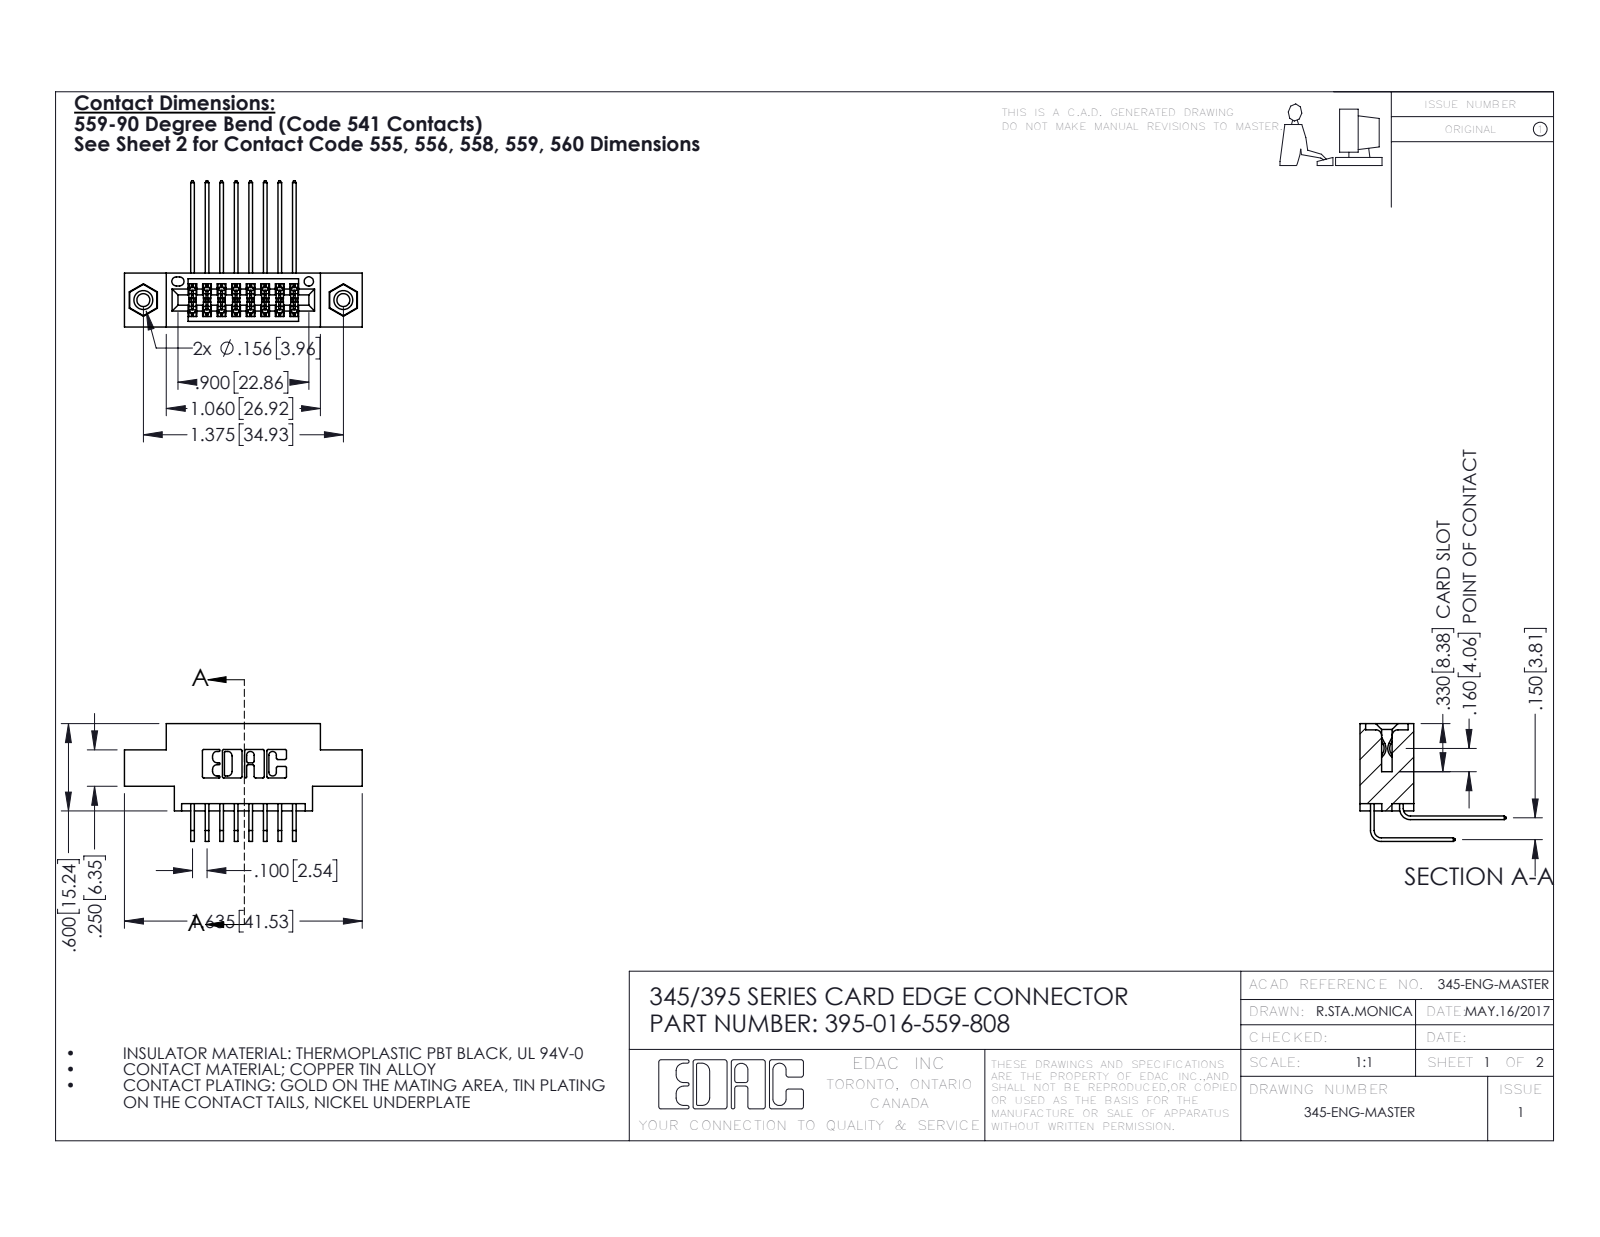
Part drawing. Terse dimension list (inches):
name: 395-016-559-808; 345-250-001_345-250-003-102; 345 Part_0.170 Offset - 0.156 Dia-TI; 345-292-001_559 Tail - 2 (+1 more)
written by: SolidWorks 2016 (CONFIG_CONTROL_DESIGN)
unit: in
bodies: 19 solids, 1022 faces (676 planar, 330 cylindrical, 16 other)
size: 1.635 × 1.005 × 0.809
volume: 0.225 in³; area: 8.352 in²
holes: 2× ⌀0.089, 2× ⌀0.125, 2× ⌀0.156, 1× ⌀0.064
bosses: 2× ⌀0.155
rounds: 25× R0.006, 22× R0.01, 6× R0.007, 6× R0.031, 3× R0.026, 2× R0.014, 2× R0.019, 2× R0.022
face distances: 0.2, 0.37, 0.072, 0.298, 0.1, 0.15, 0.098, 0.272, 0.025, 0.175
hole spacings: 0.27, 1.144, 1.375
